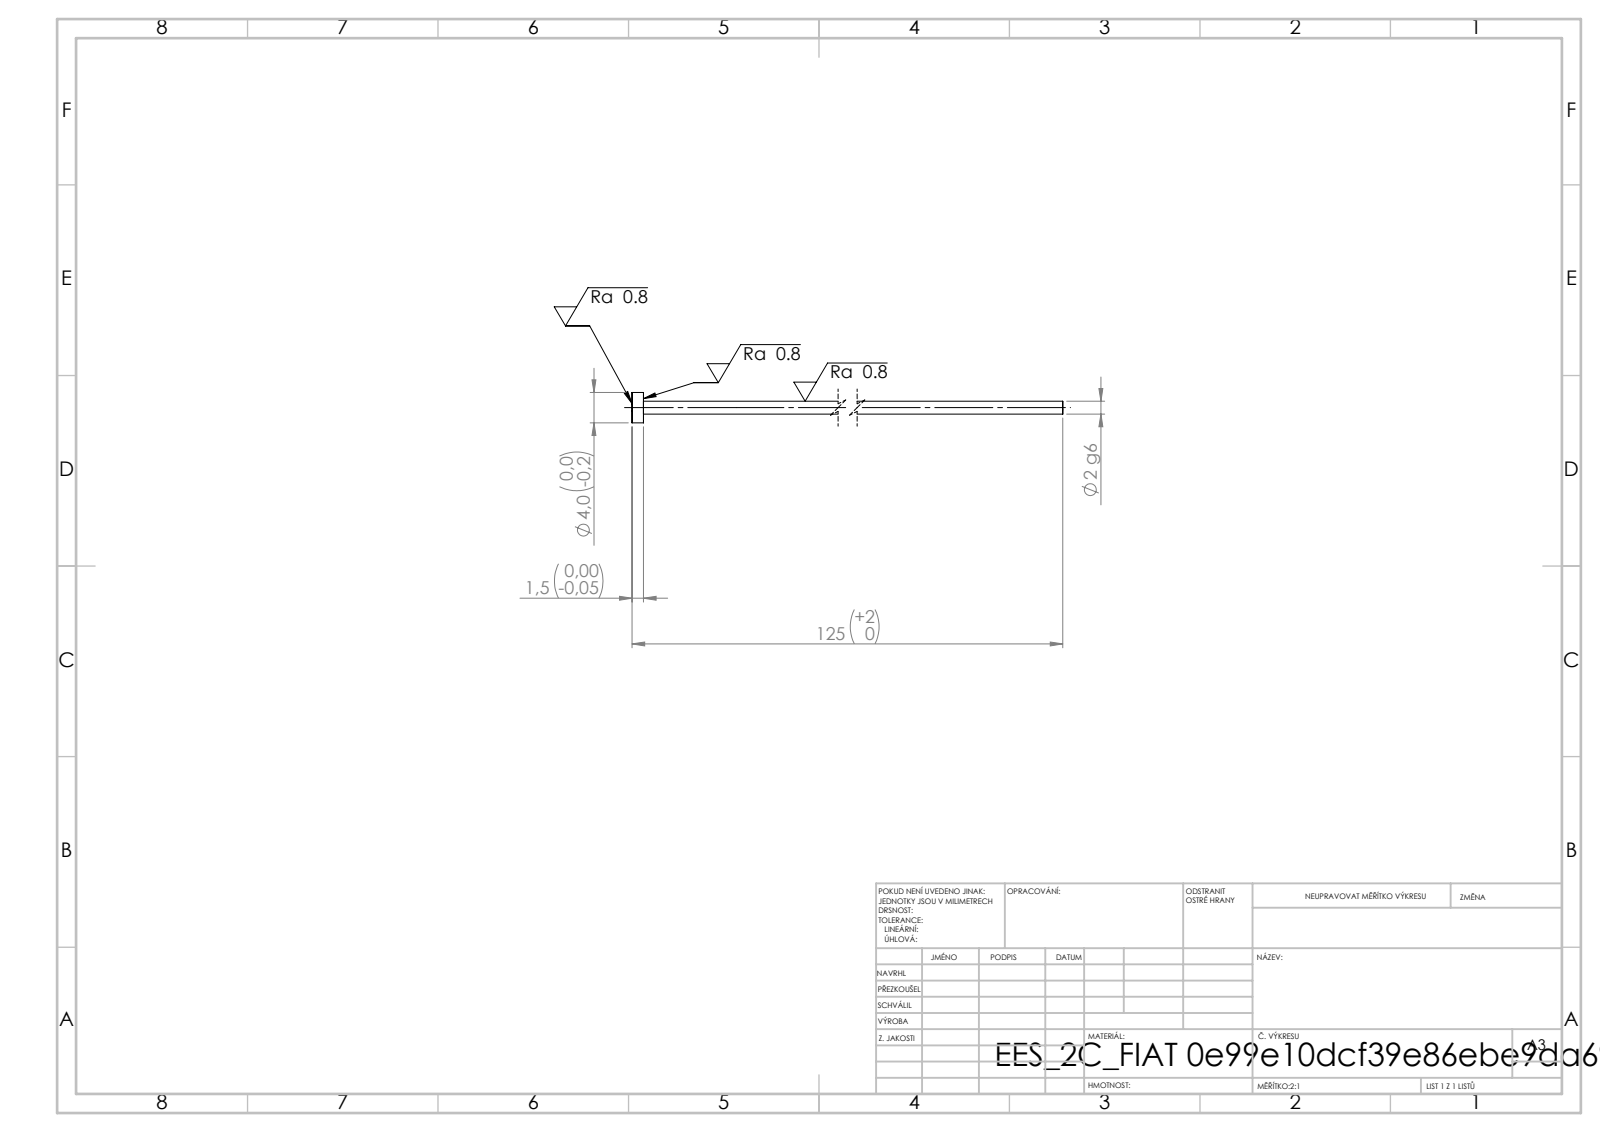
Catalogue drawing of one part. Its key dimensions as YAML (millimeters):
step_written_by: "SolidWorks 2019 (CONFIG_CONTROL_DESIGN)"
units: millimeters
bodies: {solids: 1, faces: 7, planar: 3, cylindrical: 4, other: 0}
overall_size: [125, 4, 4]
volume: 299
surface_area: 704
round_bosses_or_shafts:
  - {diameter: 4, count: 1}
  - {diameter: 1.7, count: 1}
face_to_face_distances: [1.5, 125, 123.5]
